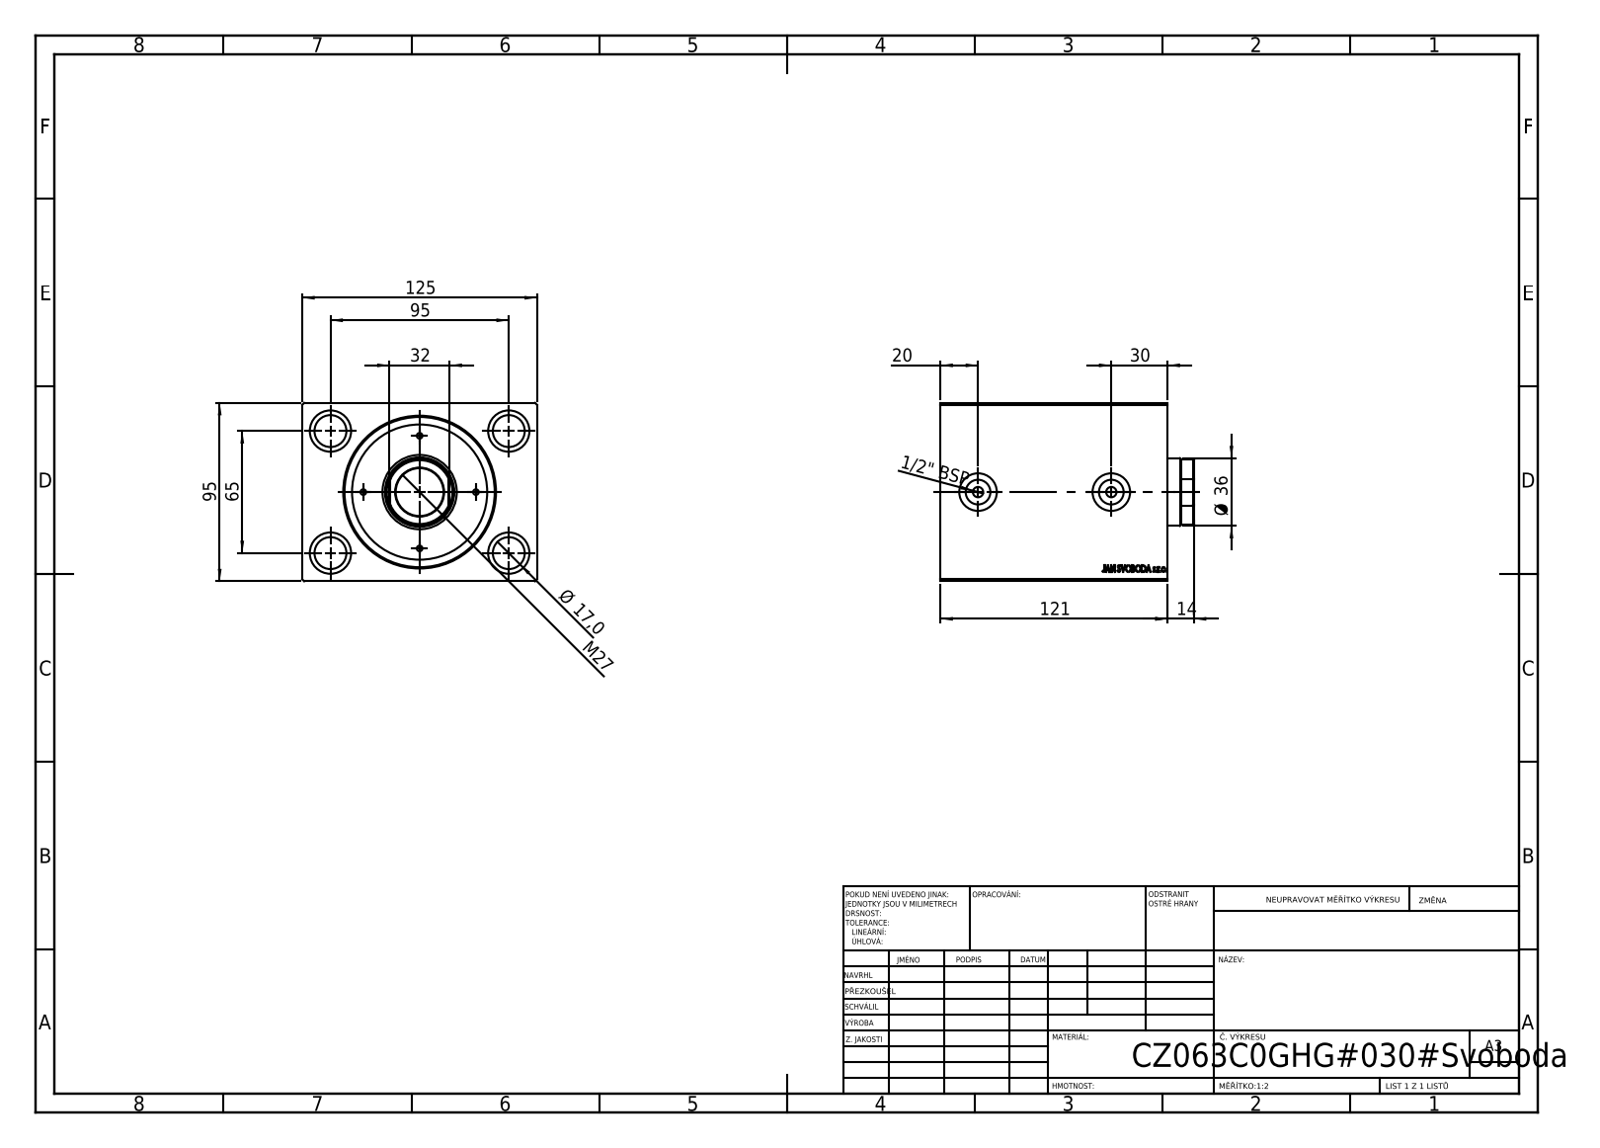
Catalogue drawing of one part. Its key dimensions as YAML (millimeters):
step_written_by: "SolidWorks 2019 (CONFIG_CONTROL_DESIGN)"
units: millimeters
bodies: {solids: 1, faces: 825, planar: 397, cylindrical: 46, other: 382}
overall_size: [125, 121, 95]
volume: 970594
surface_area: 124105
round_holes:
  - {diameter: 17, count: 4}
  - {diameter: 22, count: 4}
  - {diameter: 5.5, count: 2}
  - {diameter: 8, count: 2}
  - {diameter: 13.16, count: 2}
  - {diameter: 20, count: 2}
  - {diameter: 36, count: 1}
  - {diameter: 63, count: 1}
  - {diameter: 80, count: 1}
face_to_face_distances: [95, 125, 121, 100.2, 20.8, 14, 86.2, 107, 10.33, 110.67]
hole_center_spacings: [57.55, 65, 95, 115.11, 51, 71]
